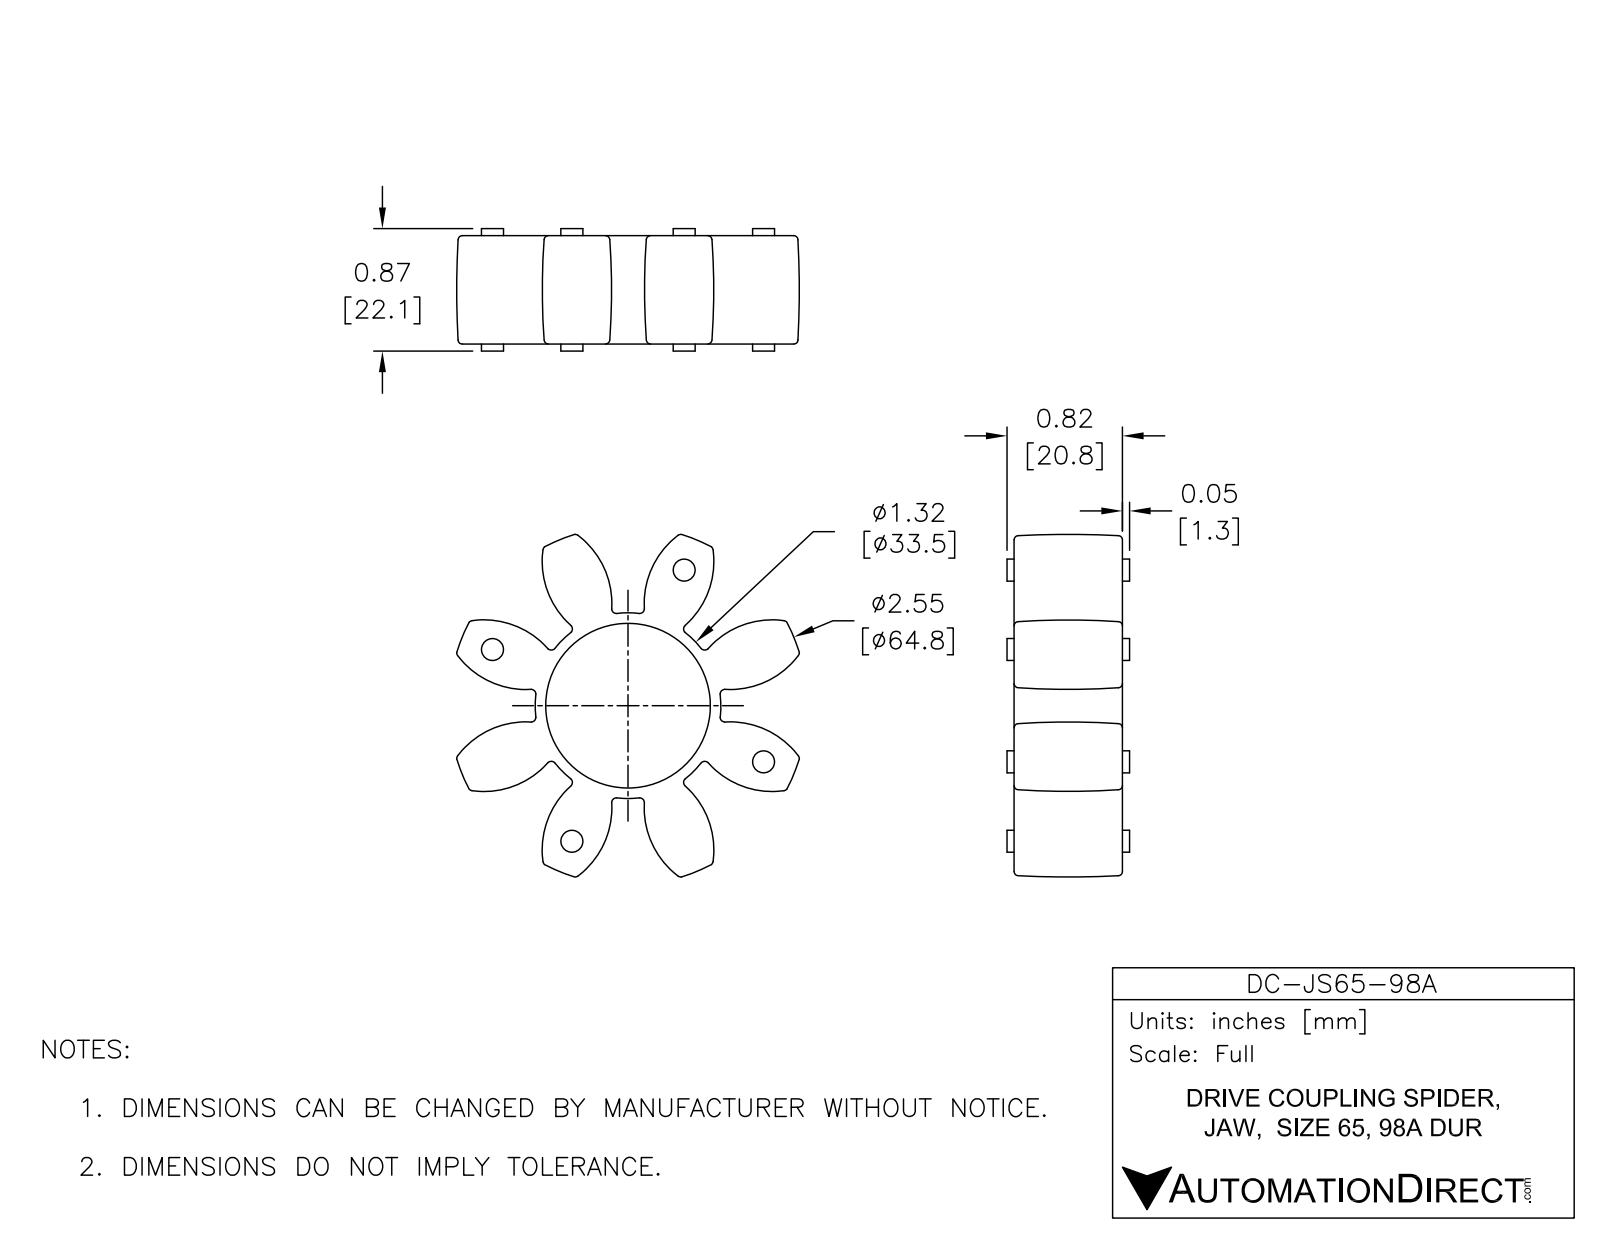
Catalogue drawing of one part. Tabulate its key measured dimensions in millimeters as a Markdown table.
| quantity | value |
| --- | --- |
| part name | DC-JS65-98A |
| STEP written by | SolidWorks 2015 (AUTOMOTIVE_DESIGN) |
| units | millimeters |
| bodies | 1 solid, 264 faces (10 planar, 58 cylindrical, 196 other) |
| overall size | 61.28 × 61.28 × 22.1 |
| volume | 25 187 mm³ |
| surface area | 11 168 mm² |
| round holes (diameter × count) | 29.72 × 1 |
| round bosses / shafts (diameter × count) | 3.96 × 8 |
| partial cylindrical surfaces (radius × count) | 0.75 × 32 |
| main face-to-face distances | 19.56, 1.27, 20.83, 22.1 |
